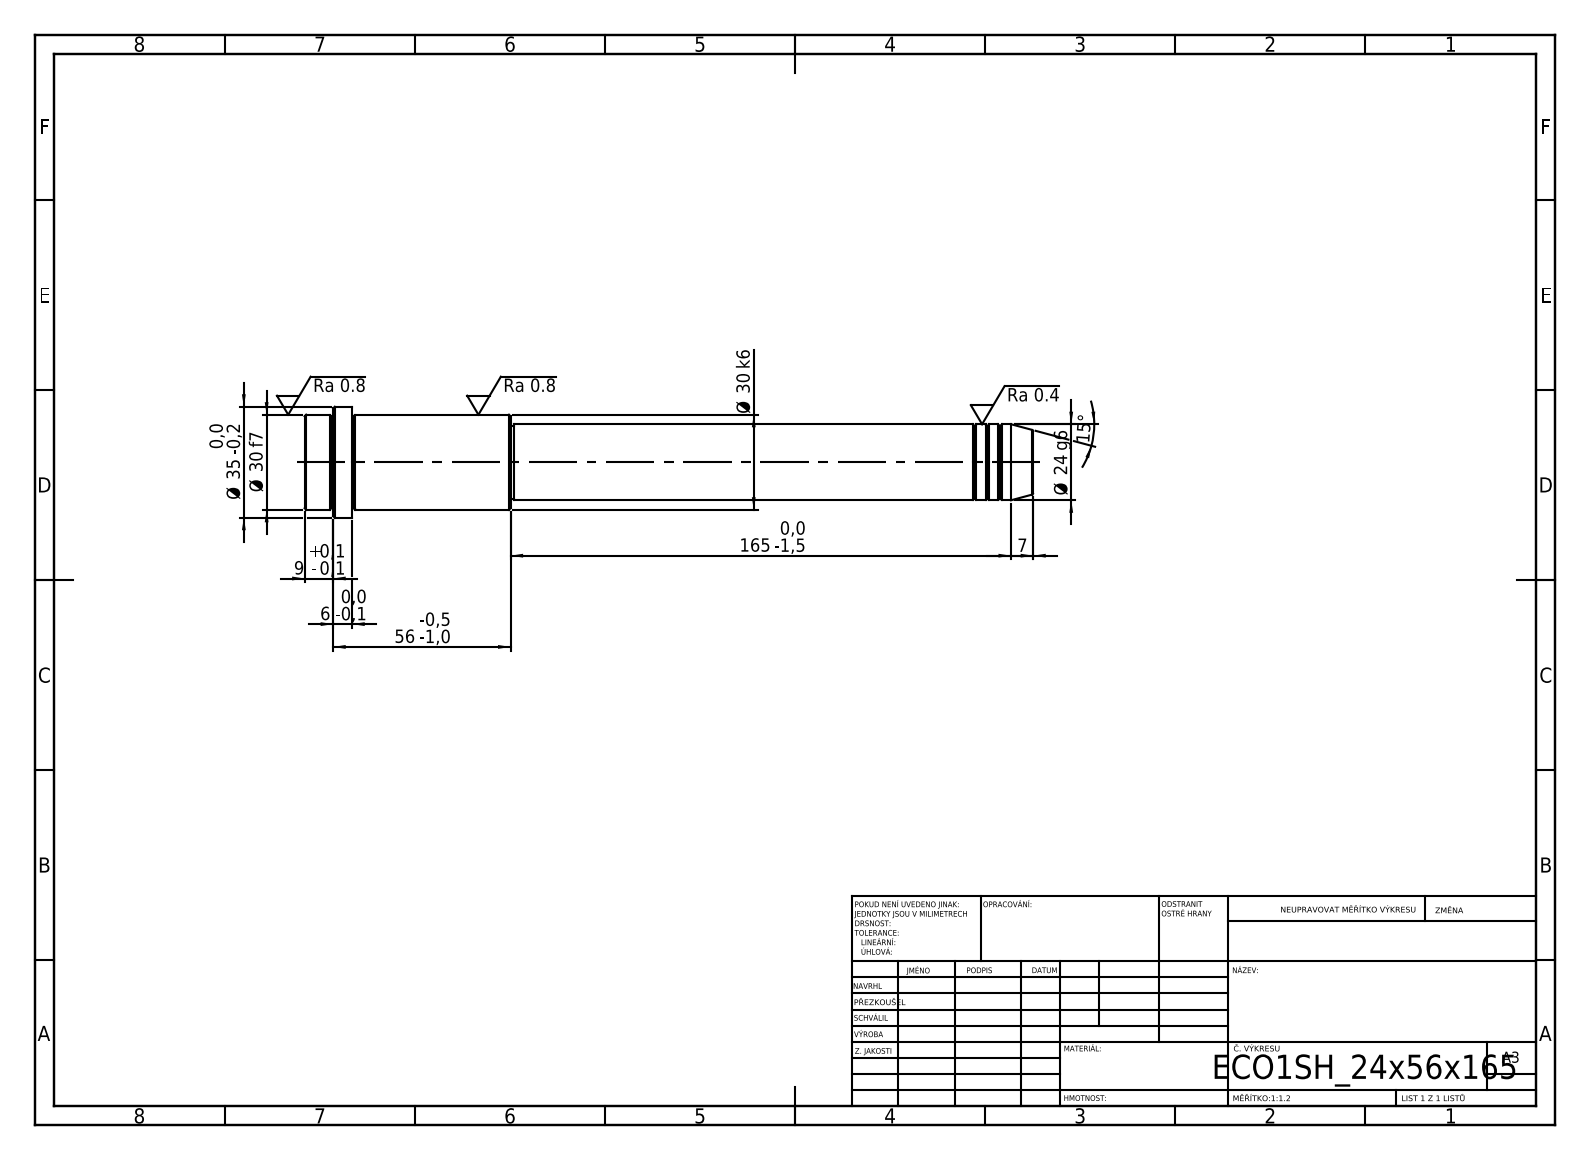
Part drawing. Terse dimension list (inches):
written by: SolidWorks 2019 (CONFIG_CONTROL_DESIGN)
unit: in
bodies: 1 solid, 52 faces (6 planar, 16 cylindrical, 30 other)
size: 9.055 × 1.378 × 1.378
volume: 7.409 in³; area: 31.97 in²
bosses: 1× ⌀1.378, 1× ⌀1.181, 1× ⌀0.945, 1× ⌀0.906
face distances: 9.055, 8.465, 0.591, 6.496, 1.969, 2.559, 8.701, 2.205, 0.236, 0.354
